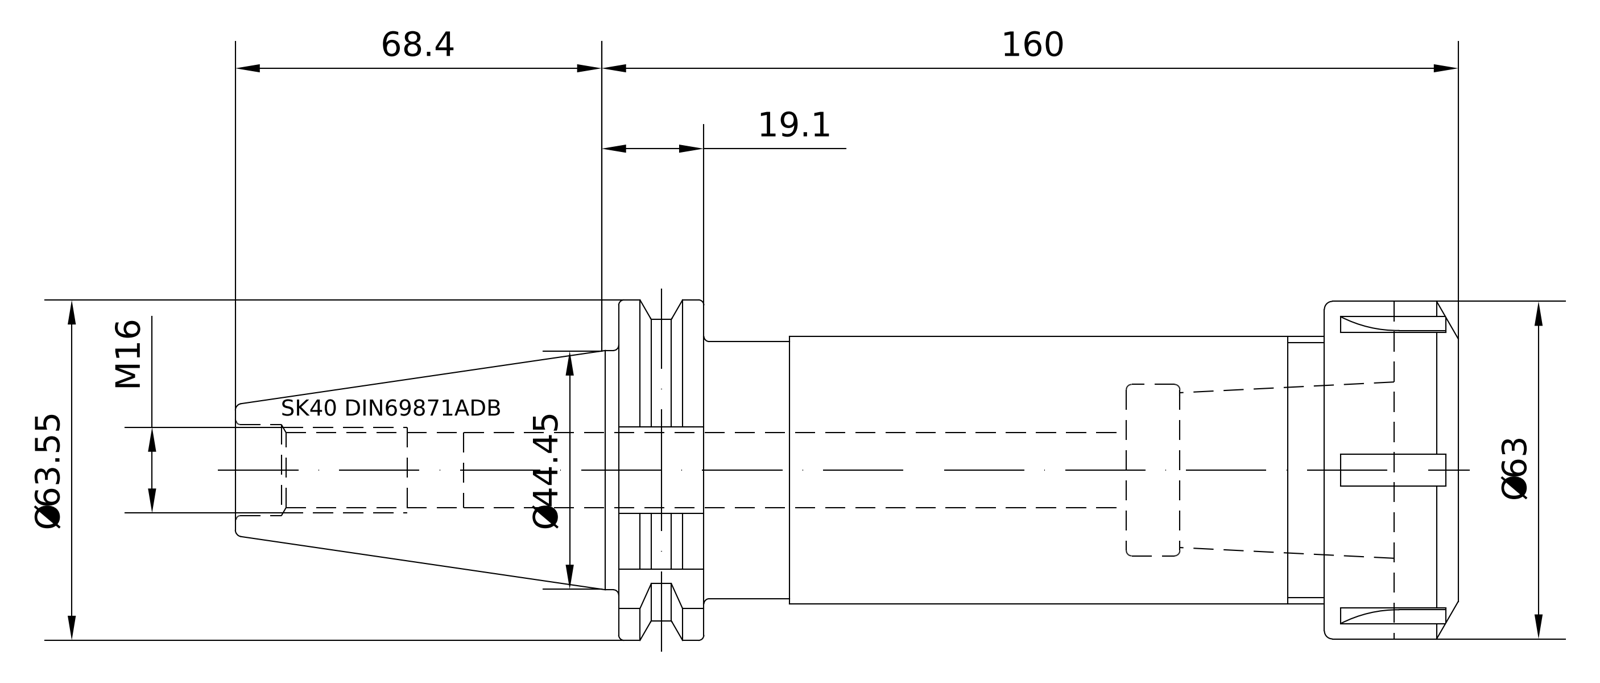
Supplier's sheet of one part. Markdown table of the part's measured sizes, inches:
| quantity | value |
| --- | --- |
| part name | 40-322-40; 83-912-40; 40-322-40_ASM |
| STEP written by | PRO/ENGINEER BY PARAMETRIC TECHNOLOGY CORPORATION, 2010430 (CONFIG_CONTROL_DESIGN) |
| units | inches |
| bodies | 2 solids, 141 faces (50 planar, 34 cylindrical, 57 other) |
| overall size | 8.986 × 2.501 × 2.48 |
| volume | 23.75 in³ |
| surface area | 84.3 in² |
| round holes (diameter × count) | 0.545 × 1, 0.67 × 1, 0.689 × 1, 1.201 × 1 |
| round bosses / shafts (diameter × count) | 2.48 × 1, 1.969 × 1, 1.87 × 1, 1.722 × 1, 0.63 × 1 |
| partial cylindrical surfaces (radius × count) | 0.106 × 6, 0.053 × 1, 1.102 × 1, 1.25 × 1 |
| main face-to-face distances | 1.004, 5.169, 6.173, 0.624, 4.545, 5.549, 4.087, 3.463, 1.083, 2.087 |
